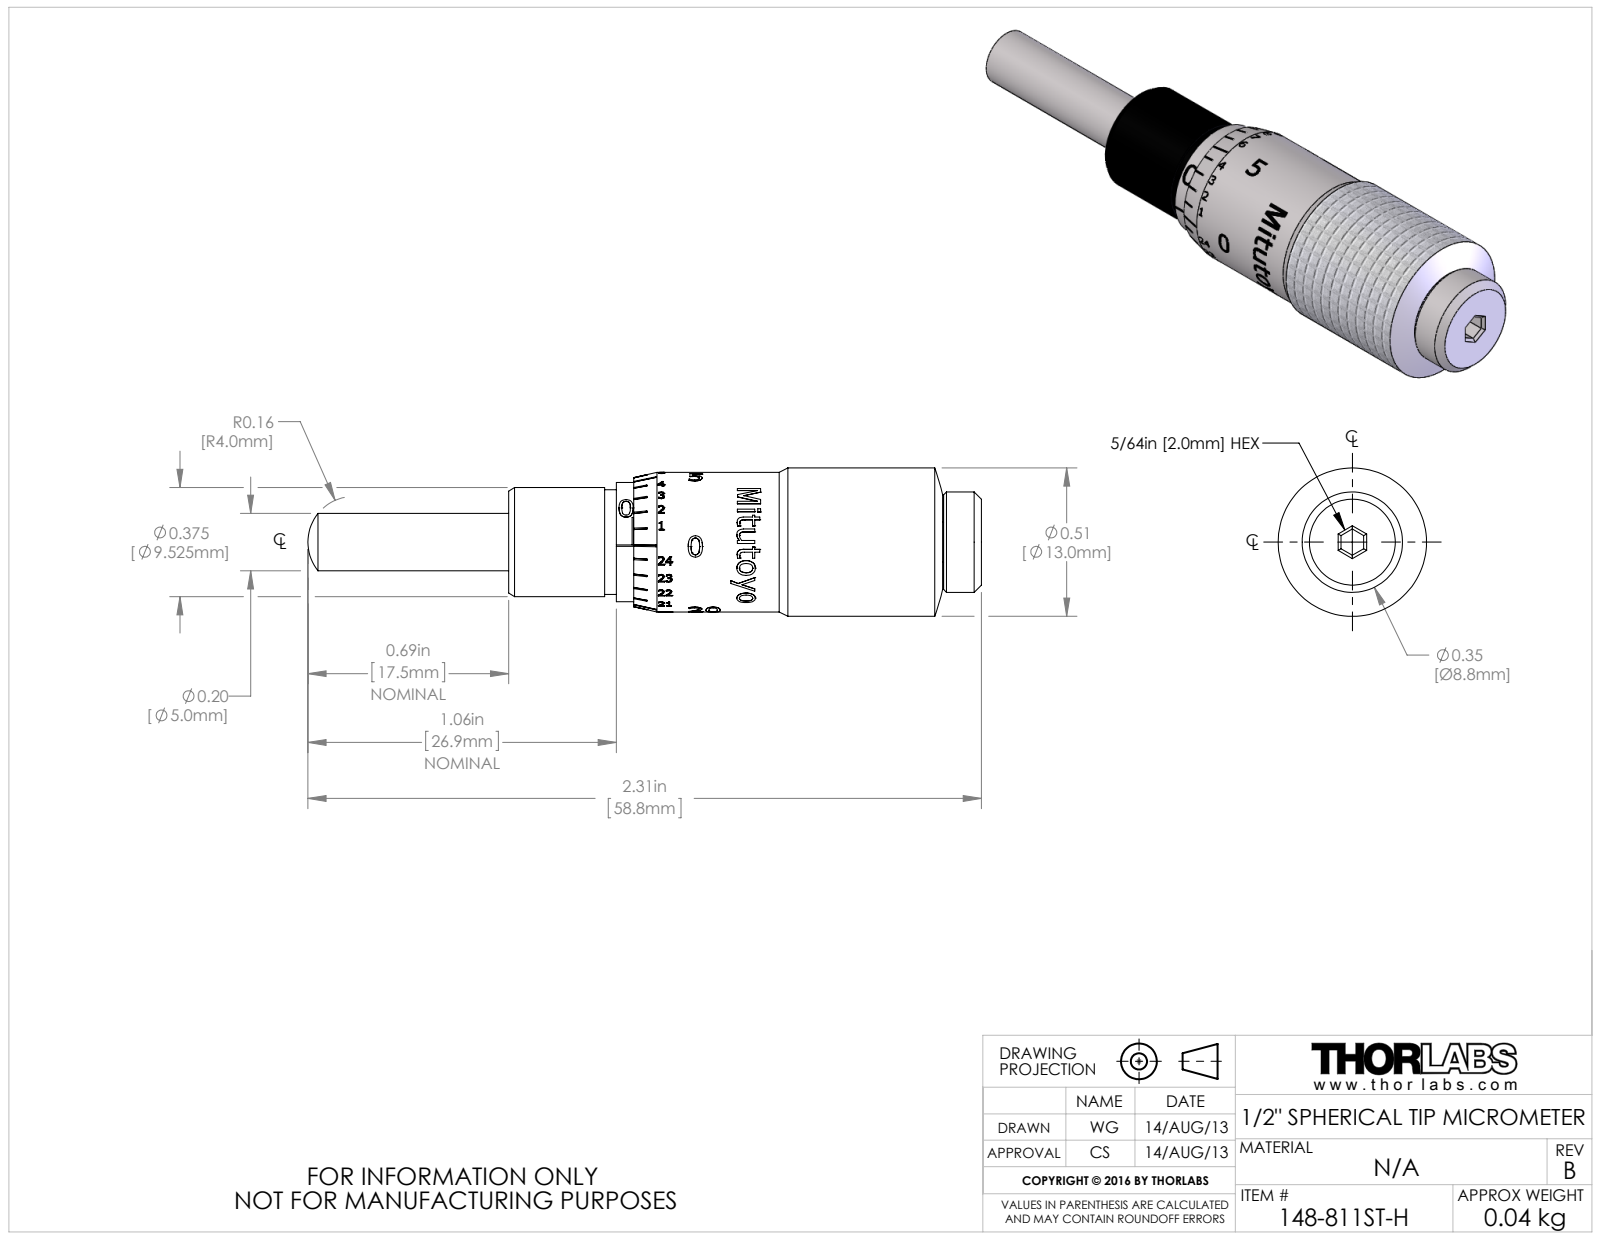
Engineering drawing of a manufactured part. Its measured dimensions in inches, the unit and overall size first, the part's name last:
Units: inches
Overall size (bounding box): 2.315 × 0.51 × 0.51
Round holes (diameter × count): ⌀0.157 ×1
Round bosses / shafts (diameter × count): ⌀0.51 ×1, ⌀0.48 ×1, ⌀0.41 ×1, ⌀0.375 ×1, ⌀0.36 ×1, ⌀0.345 ×1, ⌀0.197 ×1, ⌀0.137 ×1
Partial cylindrical surfaces — rounded edges, fillets, slot ends (radius × count): R0.205 ×1, R0.232 ×1, R0.24 ×1, R0.24 ×1
Main face-to-face distances: 1.495, 1.492, 1.625, 0.133, 0.13, 0.43, 1.195, 0.37, 1.122, 1.125
Volume: 0.282 in³ · Surface area: 3.542 in²
Bodies: 2 solids, 951 faces (414 planar, 114 cylindrical, 423 other)
Part name (STEP PRODUCT): TTN017211-E0W
STEP written by: SolidWorks 2012 (AUTOMOTIVE_DESIGN)
